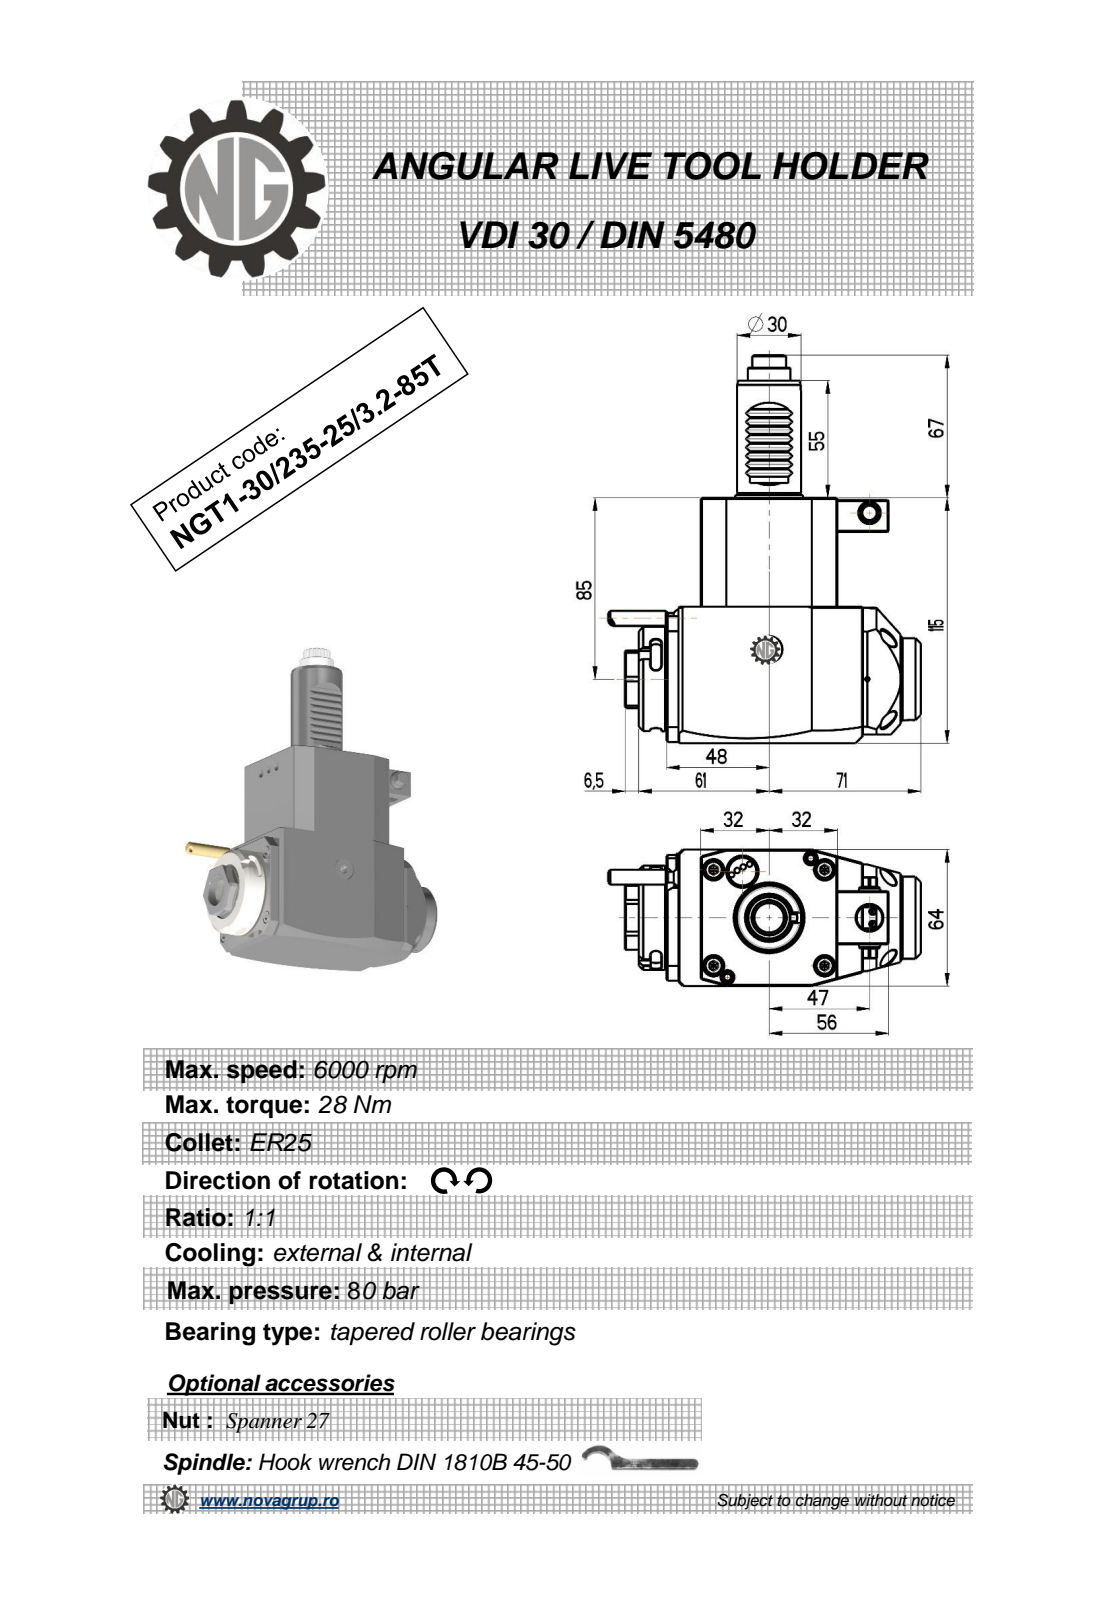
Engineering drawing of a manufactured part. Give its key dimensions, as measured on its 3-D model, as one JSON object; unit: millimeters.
{"part_name": "NGT1_30_235_25_3_2_85T", "step_written_by": "PRO/ENGINEER BY PARAMETRIC TECHNOLOGY CORPORATION, 2010280 (CONFIG_CONTROL_DESIGN)", "units": "millimeters", "bodies": {"solids": 1, "faces": 467, "planar": 213, "cylindrical": 164, "other": 90}, "overall_size": [182, 146.38, 64], "volume_mm3": 691125, "surface_area_mm2": 59106, "round_holes": [[2.5, 1], [3, 1], [9.5, 1], [12, 1], [18, 1]], "round_bosses_or_shafts": [[8, 2], [49, 1], [42, 1], [38.5, 1], [30, 1], [20, 1], [10, 1], [7, 1]], "partial_cylinders_radius": [[1.98, 36], [0.3, 8], [2.5, 6], [180, 2], [3.85, 1], [4.25, 1], [4.5, 1], [7.08, 1]], "face_to_face_distances": [64, 115, 16, 80, 51, 13, 93, 72.18, 29, 132], "hole_center_spacings": [34.25, 51.62, 76.5]}
